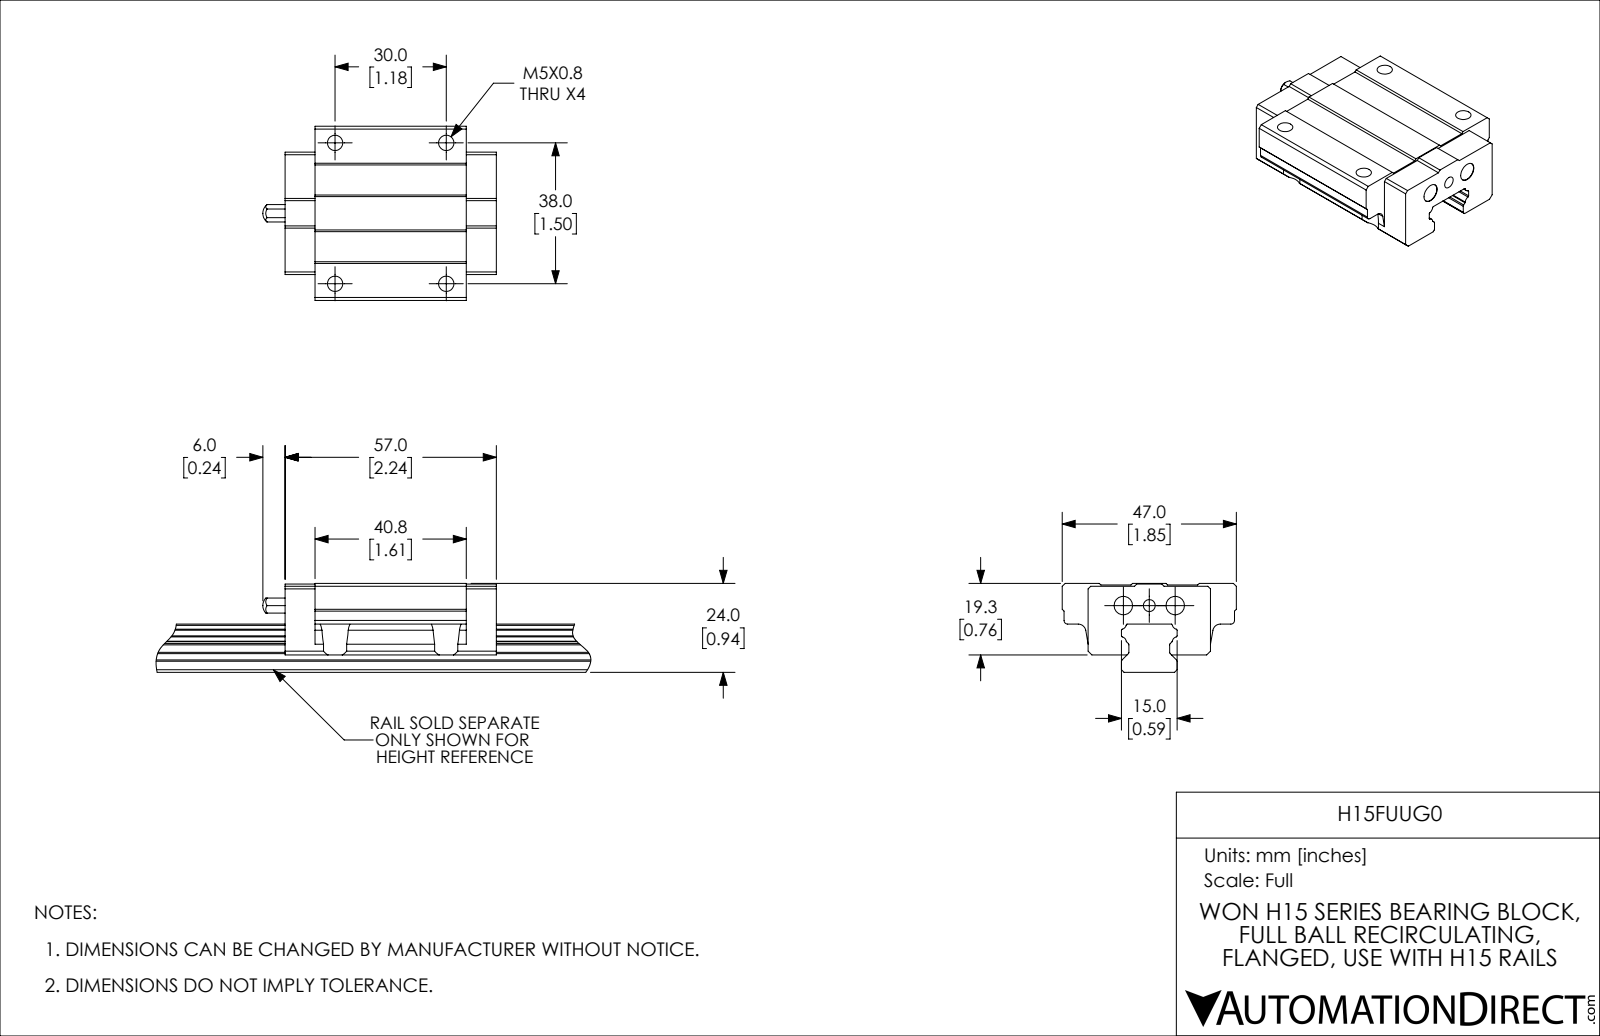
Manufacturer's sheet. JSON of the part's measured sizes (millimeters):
{"part_name": "H15FUUG0", "step_written_by": "SolidWorks 2019 (CONFIG_CONTROL_DESIGN)", "units": "millimeters", "bodies": {"solids": 2, "faces": 142, "planar": 80, "cylindrical": 58, "other": 4}, "overall_size": [63, 47, 19.3], "volume_mm3": 35075, "surface_area_mm2": 10126, "round_holes": [[4.13, 4], [5, 2], [3.24, 1]], "round_bosses_or_shafts": [[4, 1]], "partial_cylinders_radius": [[0.3, 6], [0.5, 4], [1.4, 4], [4, 4], [0.6, 2], [1, 2], [2, 1], [2.01, 1]], "face_to_face_distances": [11, 19.3, 8.3, 18.85, 10.55, 0.45, 7, 40, 57, 18.5], "hole_center_spacings": [7, 30, 38, 48.41, 14]}
